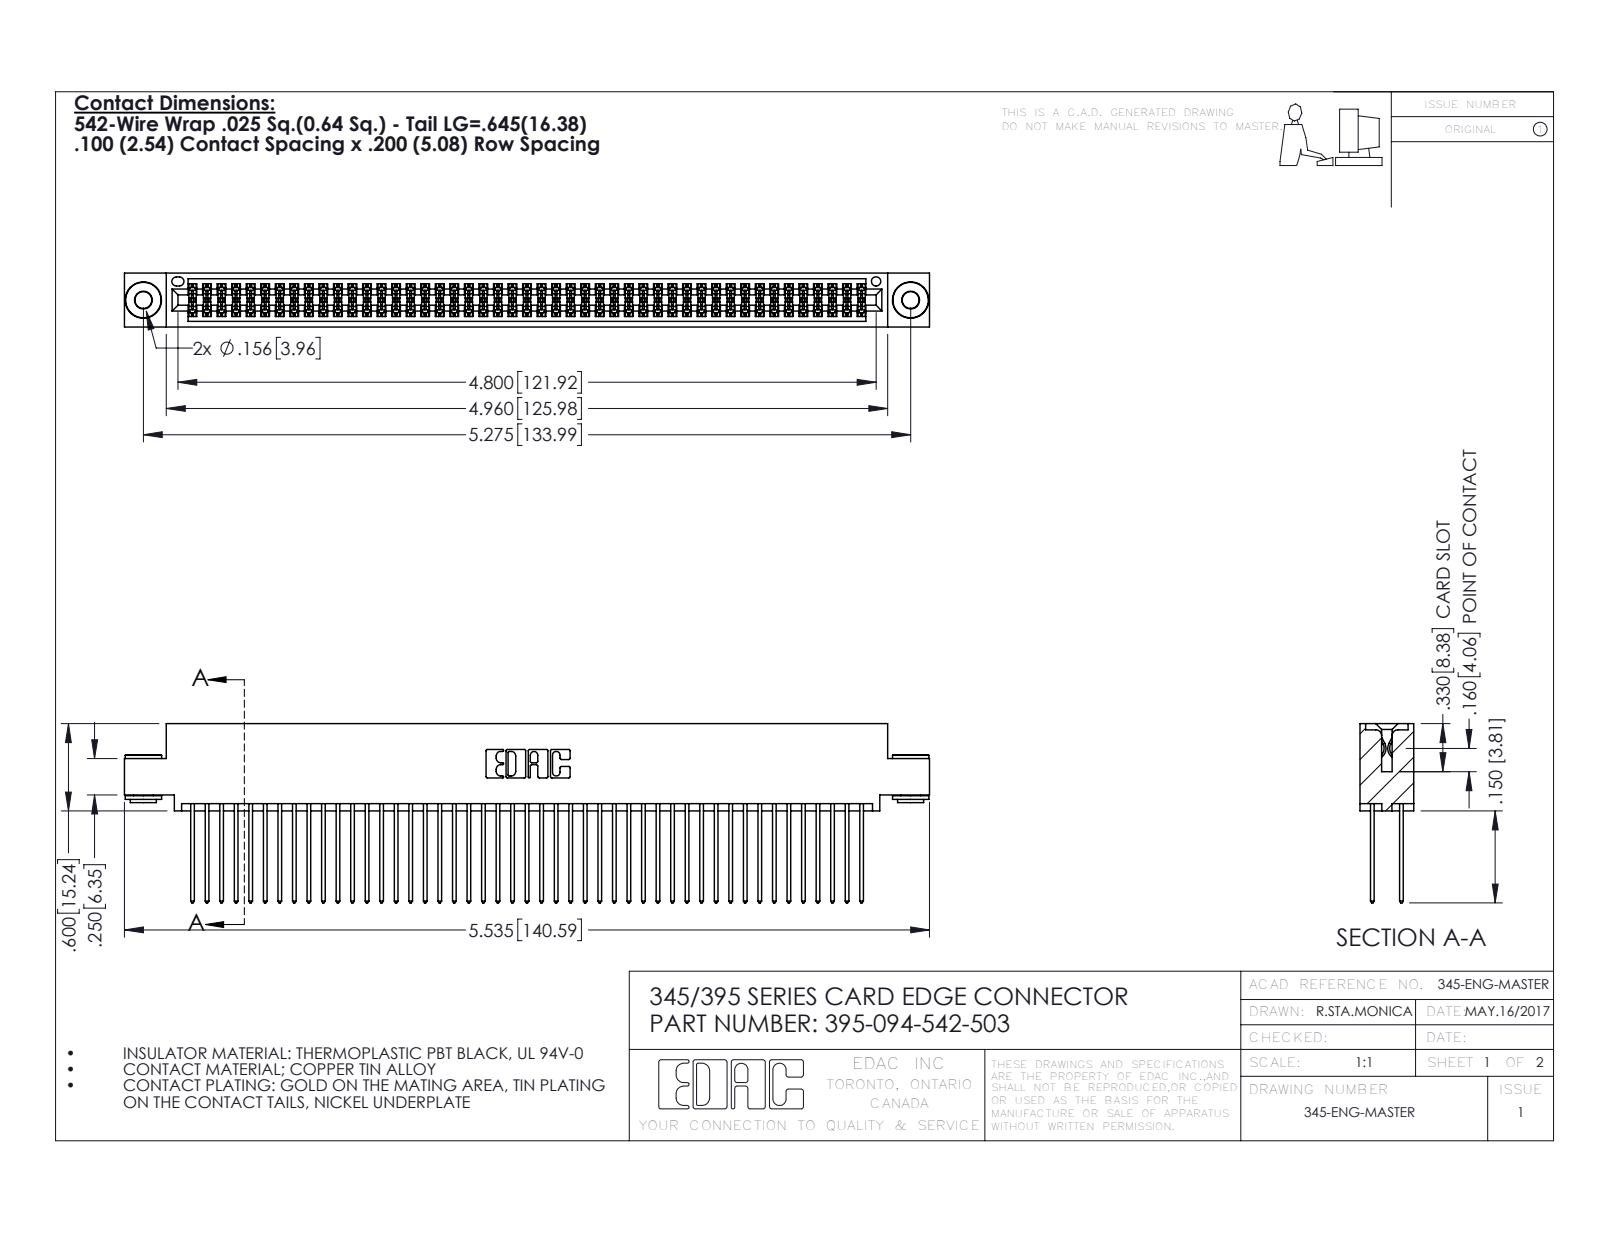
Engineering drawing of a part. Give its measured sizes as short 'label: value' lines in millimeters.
name: 395-094-542-503; 345-250-002_345-250-002-102; 345 Part_0.110 Offset - 0.156 Dia-TH; 345-292-001_345-293-142
written by: SolidWorks 2016 (CONFIG_CONTROL_DESIGN)
unit: mm
bodies: 97 solids, 4868 faces (3196 planar, 1664 cylindrical, 8 other)
size: 140.6 × 31.3 × 9.4
volume: 14 100 mm³; area: 23 260 mm²
holes: 2× ⌀2.9, 2× ⌀4, 1× ⌀1.6
bosses: 2× ⌀6.4, 2× ⌀4.6, 2× ⌀3.5
rounds: 141× R0.2, 94× R0.3, 22× R0.3, 6× R0.2, 6× R0.8, 3× R0.7, 2× R0.4, 2× R0.5
face distances: 1.8, 7.6, 5.1, 0.6, 2.5, 6.9, 5.7, 9.4, 4.4, 3.8
hole spacings: 6.9, 128, 134
